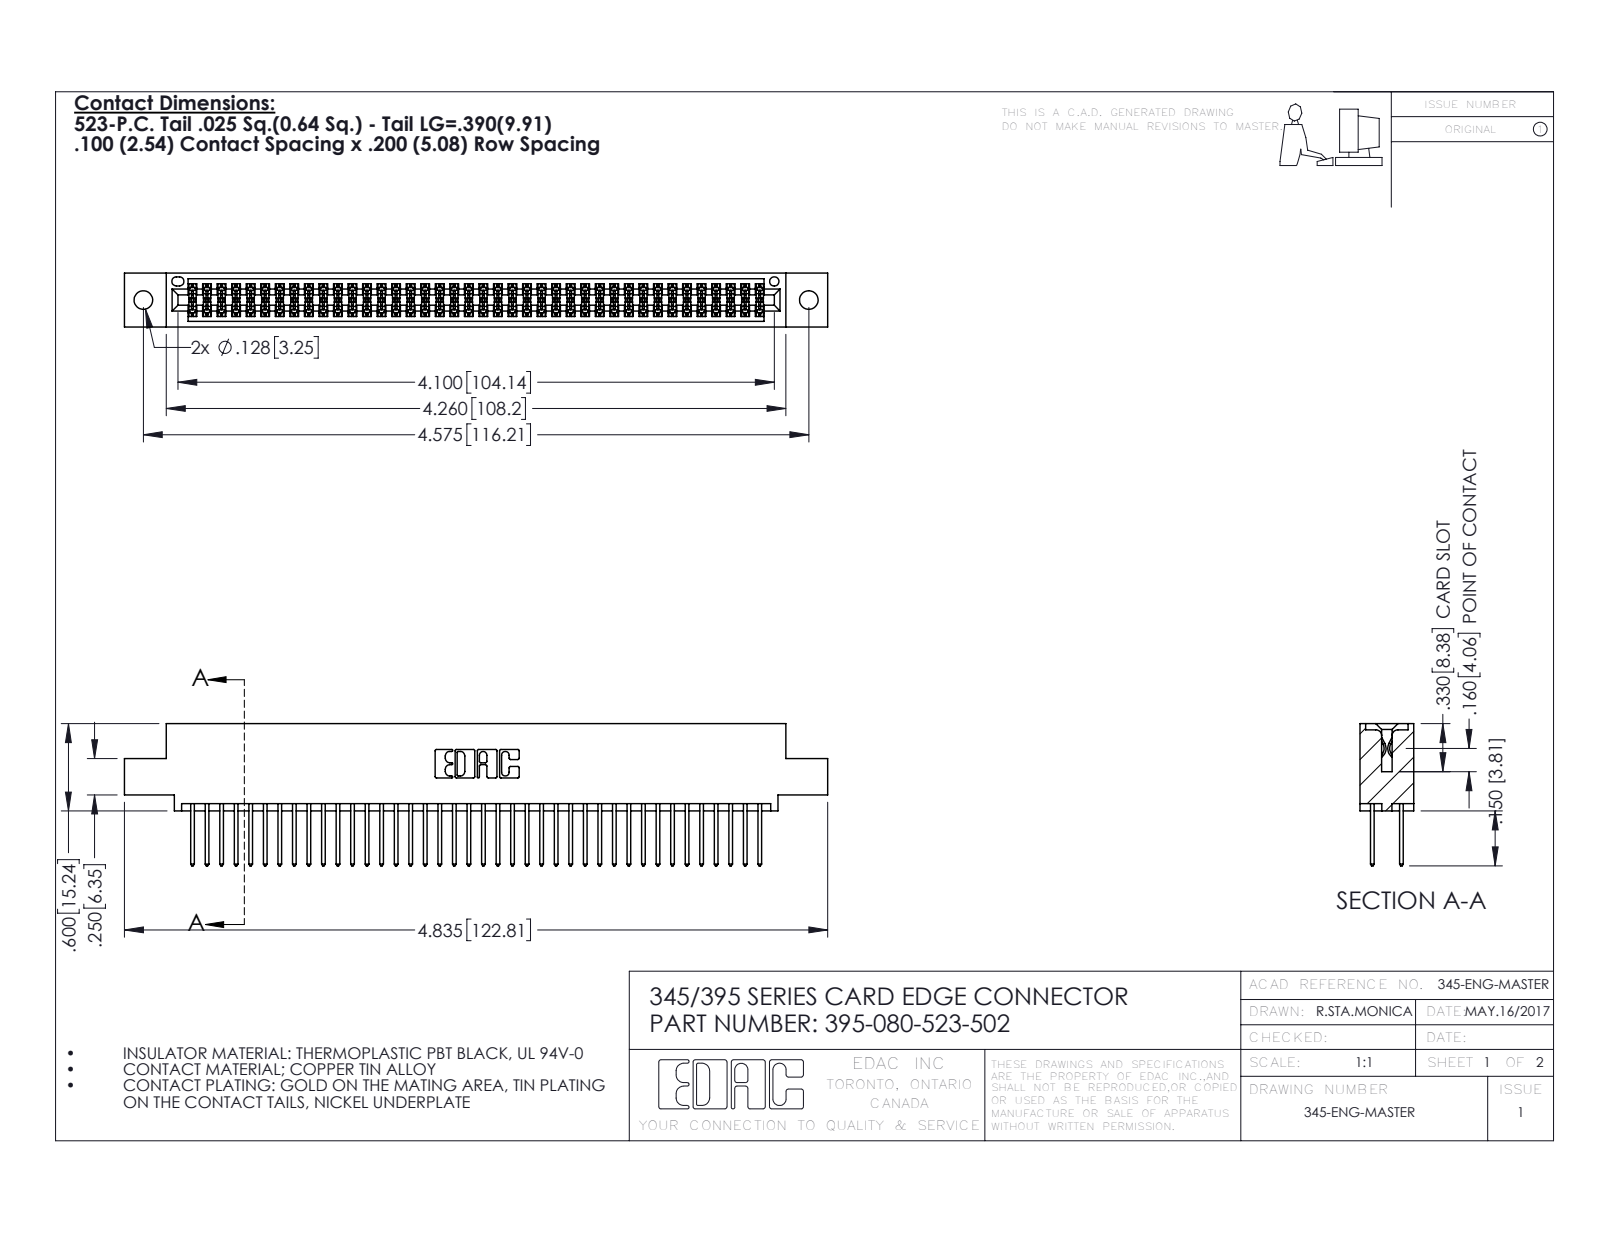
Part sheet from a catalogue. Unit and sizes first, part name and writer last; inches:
Units: inches
Overall size (bounding box): 4.835 × 0.977 × 0.37
Round holes (diameter × count): ⌀0.128 ×2, ⌀0.064 ×1
Partial cylindrical surfaces — rounded edges, fillets, slot ends (radius × count): R0.006 ×120, R0.01 ×80, R0.01 ×22, R0.007 ×6, R0.031 ×6, R0.026 ×3, R0.014 ×2, R0.019 ×2
Main face-to-face distances: 0.298, 0.072, 0.2, 0.098, 0.272, 0.025, 0.37, 0.225, 0.175, 0.149
Hole centre spacings: 0.27, 4.339, 4.575
Volume: 0.73 in³ · Surface area: 28.22 in²
Bodies: 81 solids, 4130 faces (2724 planar, 1406 cylindrical, 0 other)
Part name (STEP PRODUCT): 345 Part_0.110 Offset - 0.128 Dia; 345-292-001_345-293-123; 395-080-523-502
STEP written by: SolidWorks 2016 (CONFIG_CONTROL_DESIGN)
